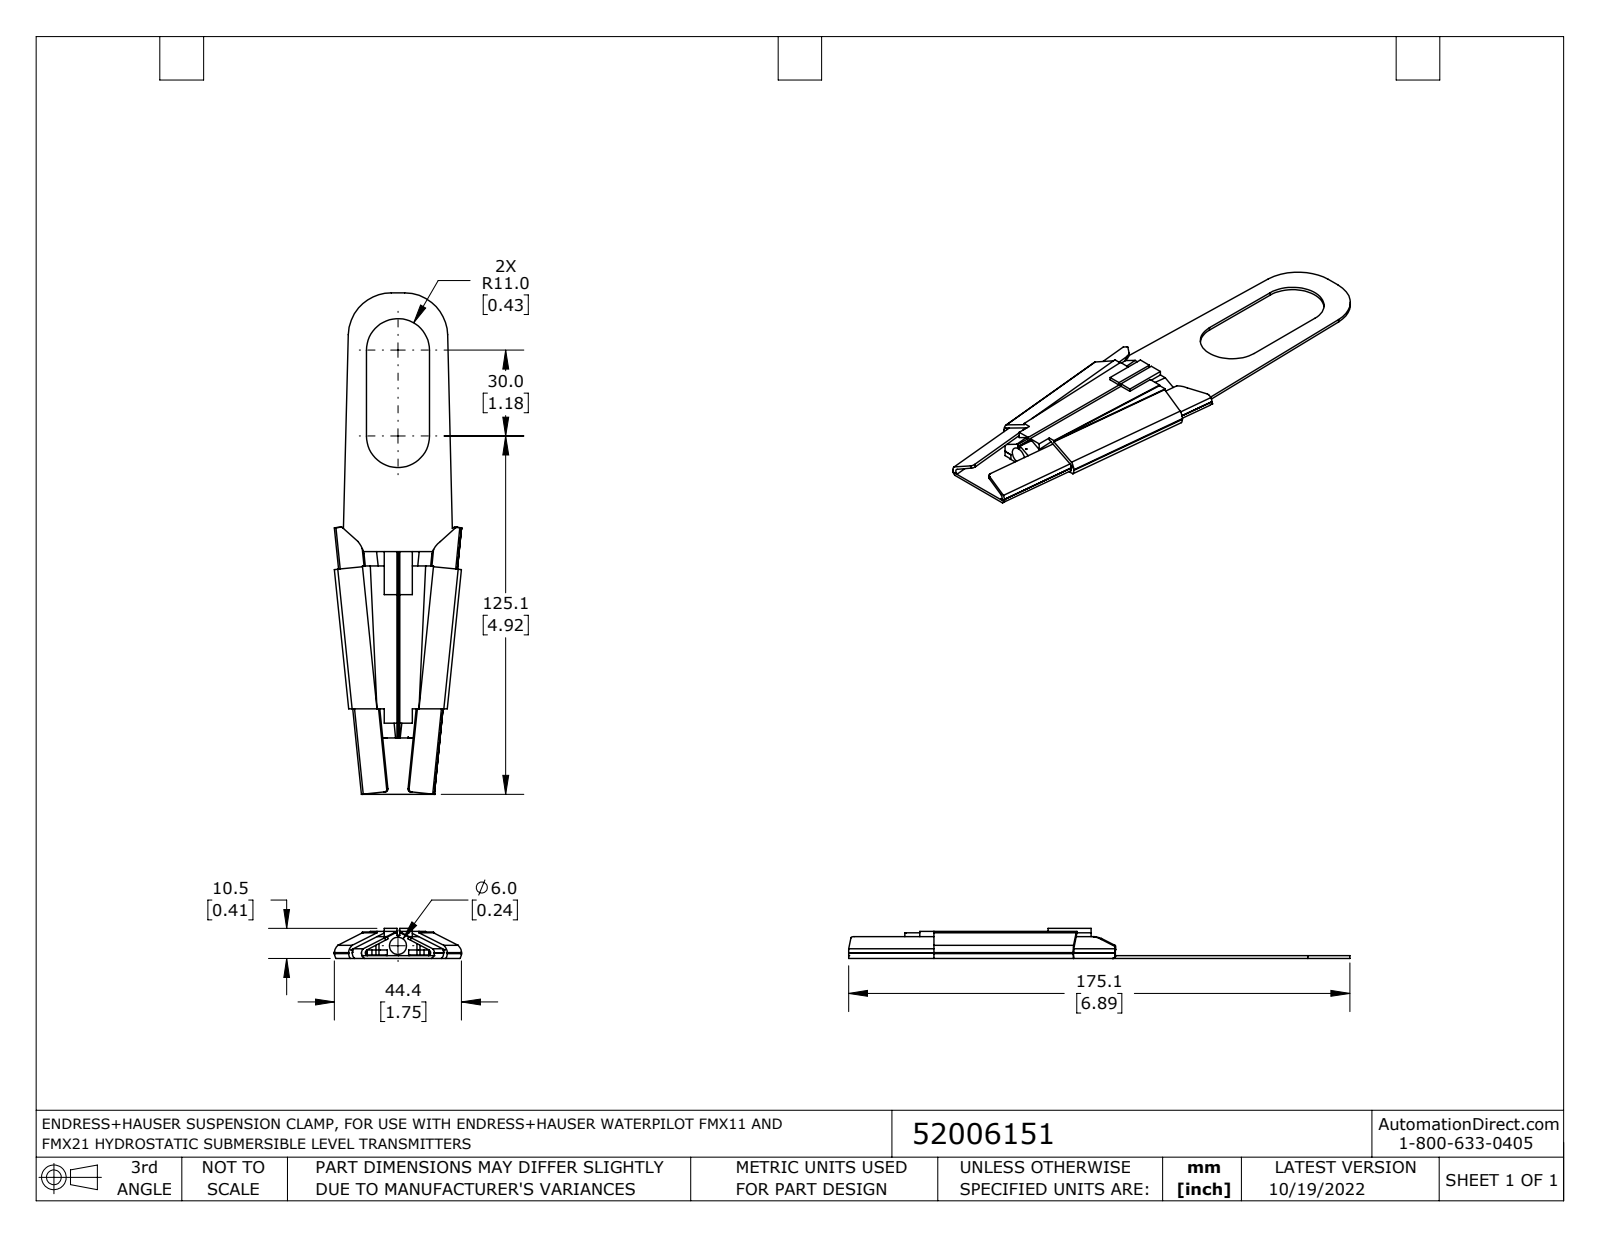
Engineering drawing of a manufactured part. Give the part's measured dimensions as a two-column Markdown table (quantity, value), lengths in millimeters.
| quantity | value |
| --- | --- |
| part name | 52006151de fxt |
| STEP written by | SolidWorks 2021 (AUTOMOTIVE_DESIGN) |
| units | millimeters |
| bodies | 4 solids, 158 faces (111 planar, 32 cylindrical, 15 other) |
| overall size | 175.06 × 44.44 × 10.5 |
| volume | 19 091 mm³ |
| surface area | 25 096 mm² |
| round holes (diameter × count) | 6 × 1 |
| partial cylindrical surfaces (radius × count) | 1 × 4, 0.86 × 2, 1.06 × 2, 1.58 × 2, 2.26 × 2, 2.46 × 2, 3.71 × 2, 11 × 2 |
| main face-to-face distances | 1, 1.25, 1.19, 1.45, 9.5, 8.5, 8.31, 9, 8, 7.81 |
